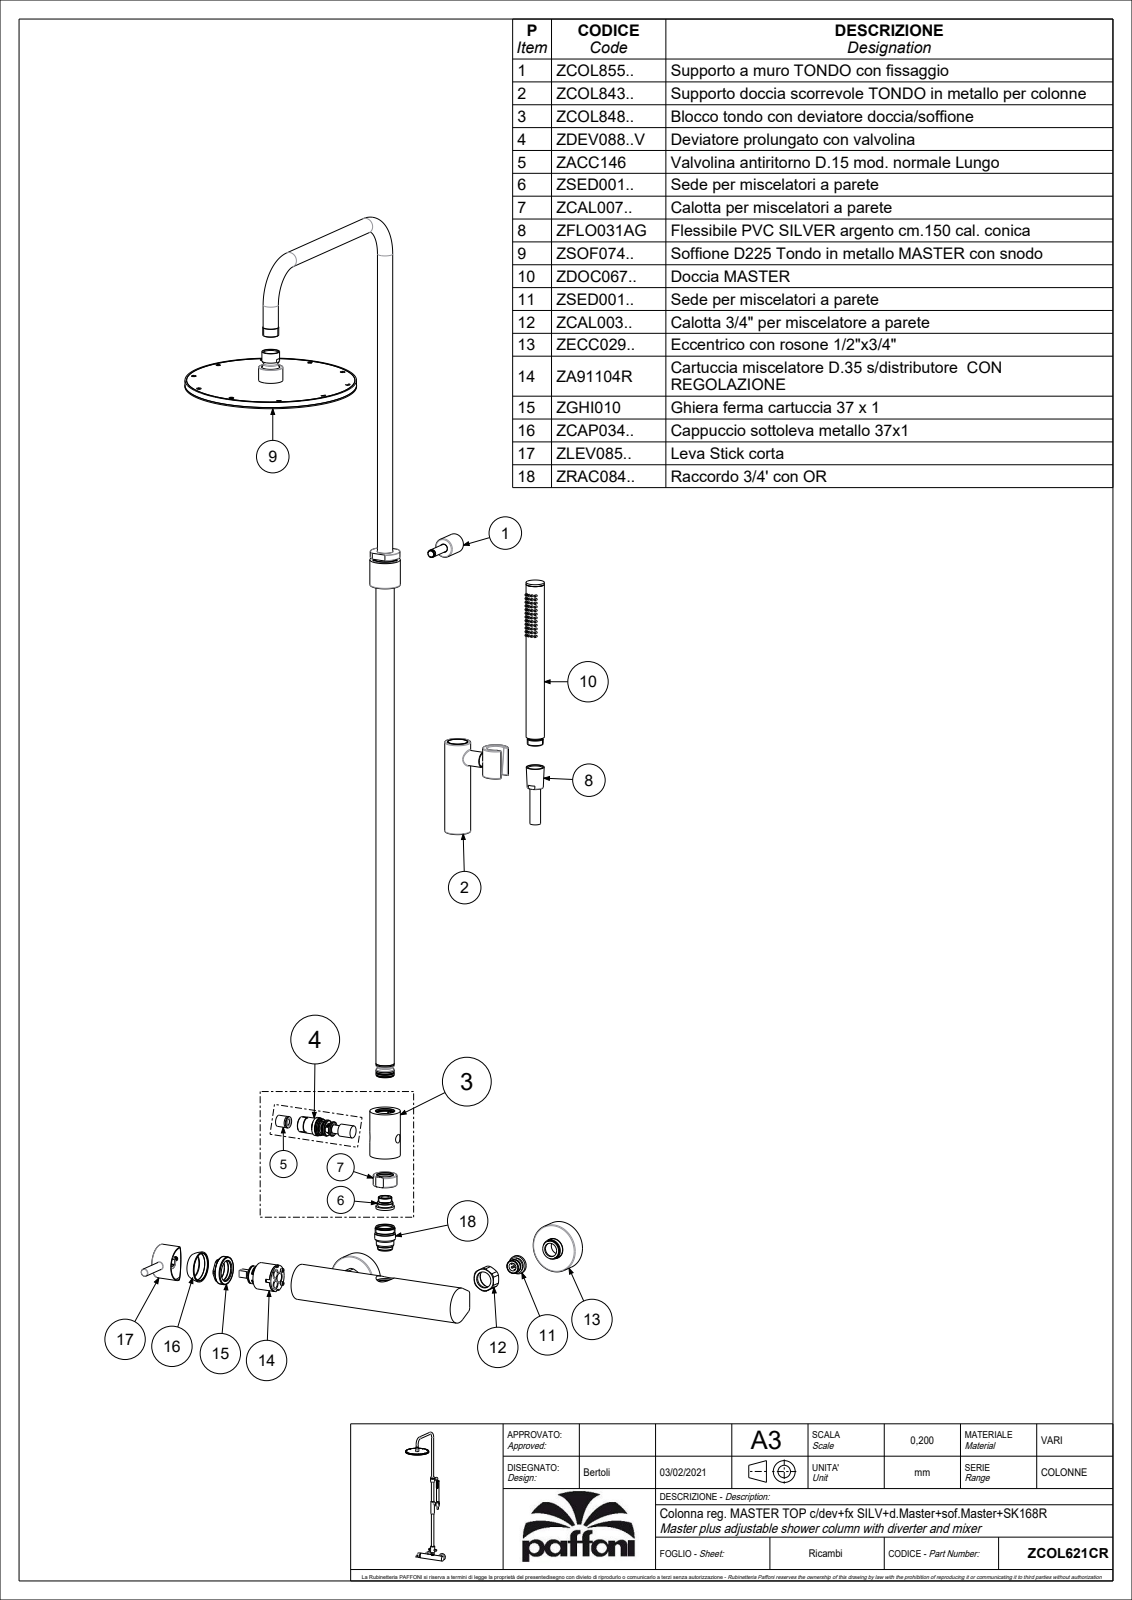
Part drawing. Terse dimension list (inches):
name: ZCOL621CR
written by: CREO PARAMETRIC BY PTC INC, 2020044 (CONFIG_CONTROL_DESIGN)
unit: in
bodies: 11 solids, 2294 faces (766 planar, 784 cylindrical, 744 other)
size: 51.209 × 19.343 × 10.775
volume: 59.02 in³; area: 873.7 in²
holes: 80× ⌀0.047, 48× ⌀0.039, 7× ⌀0.197, 4× ⌀0.413, 4× ⌀0.669, 4× ⌀0.984, 3× ⌀0.138, 3× ⌀0.276, 3× ⌀0.394, 3× ⌀0.63, 2× ⌀0.13, 2× ⌀0.177
bosses: 5× ⌀0.945, 4× ⌀0.787, 3× ⌀0.906, 2× ⌀2.5, 2× ⌀1.102, 2× ⌀1.063, 2× ⌀0.827, 2× ⌀0.728
rounds: 45× R0.059, 24× R0.012, 8× R0.02, 6× R0.039, 2× R0.051, 2× R0.197, 2× R0.61, 2× R0.728
face distances: 0.256, 0.146, 0.024, 0.138, 1.173, 1.15, 0.559, 0.413, 1.012, 1.035
hole spacings: 0.432, 0.807, 0.53, 0.394, 1.109, 3.543, 0.177, 0.863
